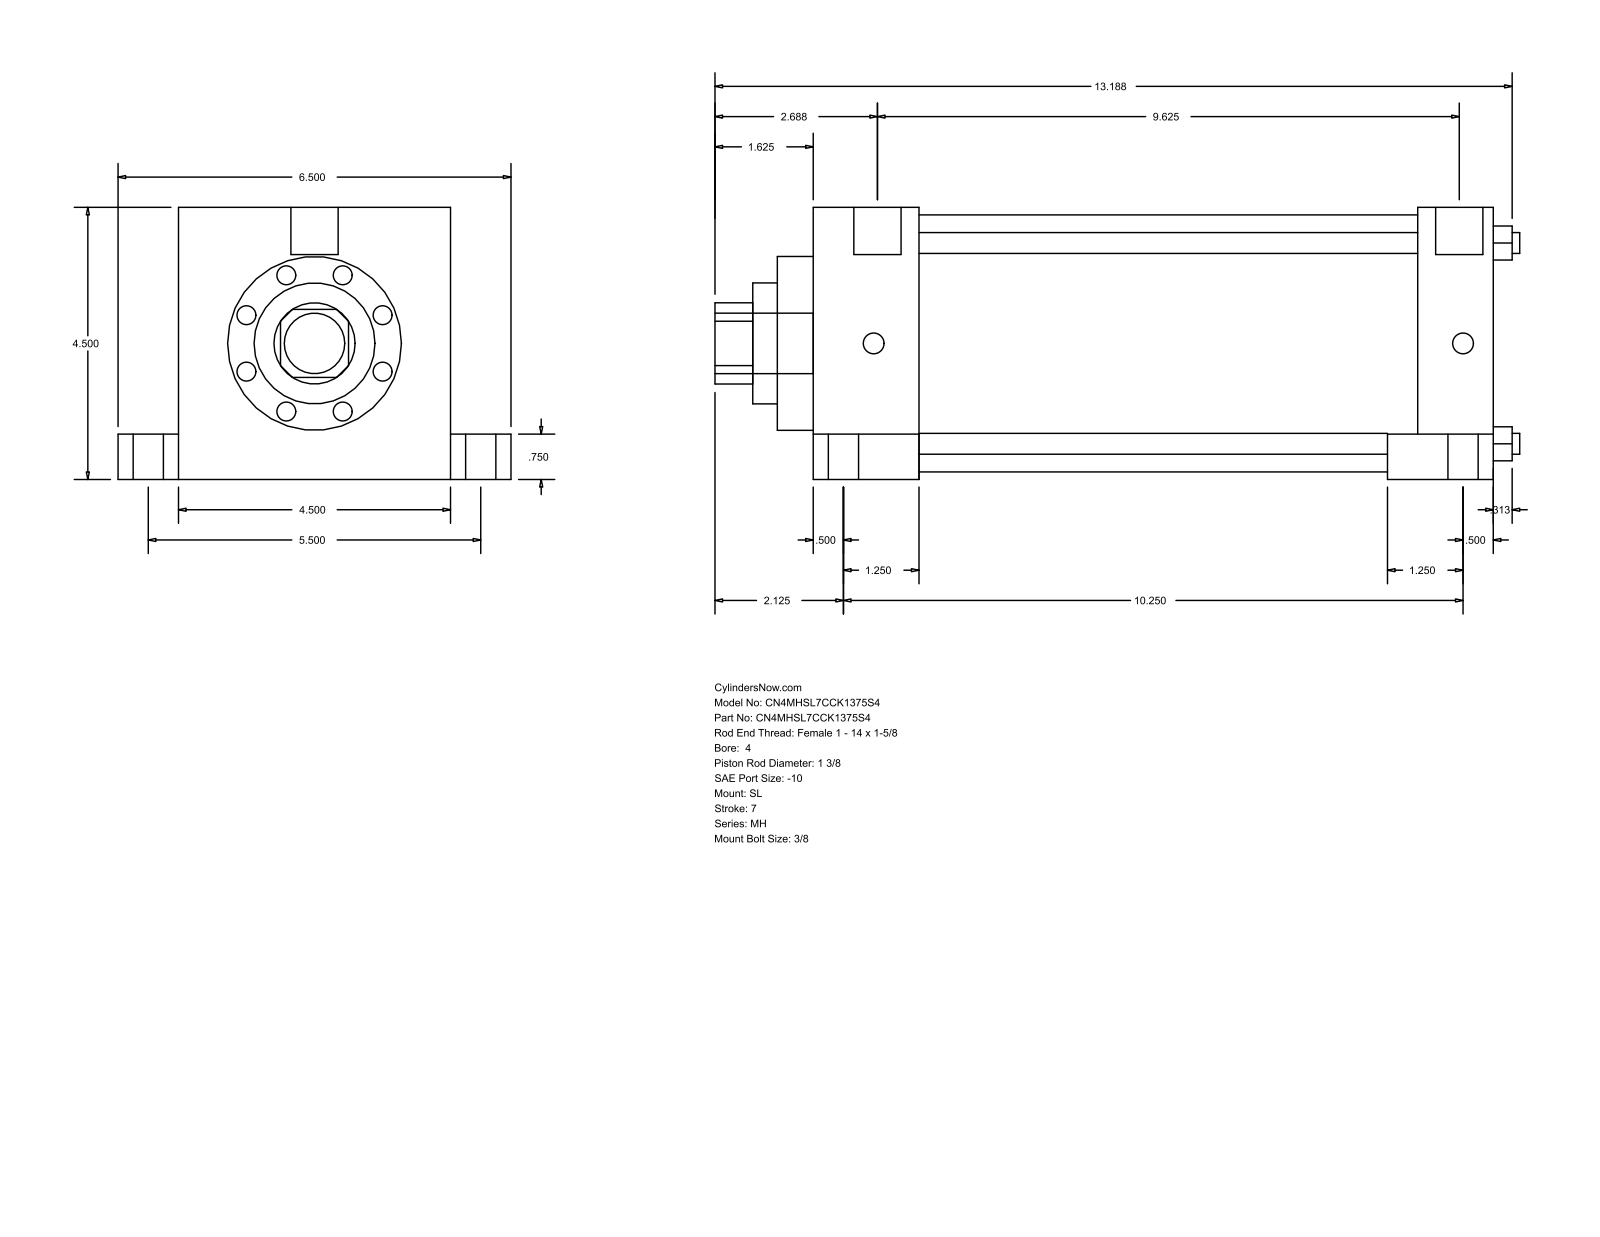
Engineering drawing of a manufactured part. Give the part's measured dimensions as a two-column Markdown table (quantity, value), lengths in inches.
| quantity | value |
| --- | --- |
| part name | MH_SL__0400_1.375 |
| STEP written by | GSSL Pune (CONFIG_CONTROL_DESIGN) |
| units | inches |
| bodies | 0 solids, 110 faces (77 planar, 33 cylindrical, 0 other) |
| overall size | 13.313 × 6.5 × 4.5 |
| round holes (diameter × count) | 0.345 × 4, 1.375 × 1, 2 × 1, 2.875 × 1, 4.25 × 1 |
| round bosses / shafts (diameter × count) | 0.75 × 4, 0.5 × 4, 0.344 × 4, 0.781 × 2, 1 × 1 |
| partial cylindrical surfaces (radius × count) | 0.672 × 1 |
| main face-to-face distances | 4.5, 11.25, 1.75, 9.5, 10, 8.25, 1.25, 1, 5.5, 0.75 |
| hole center spacings | 2.347, 3.32, 4.695 |
